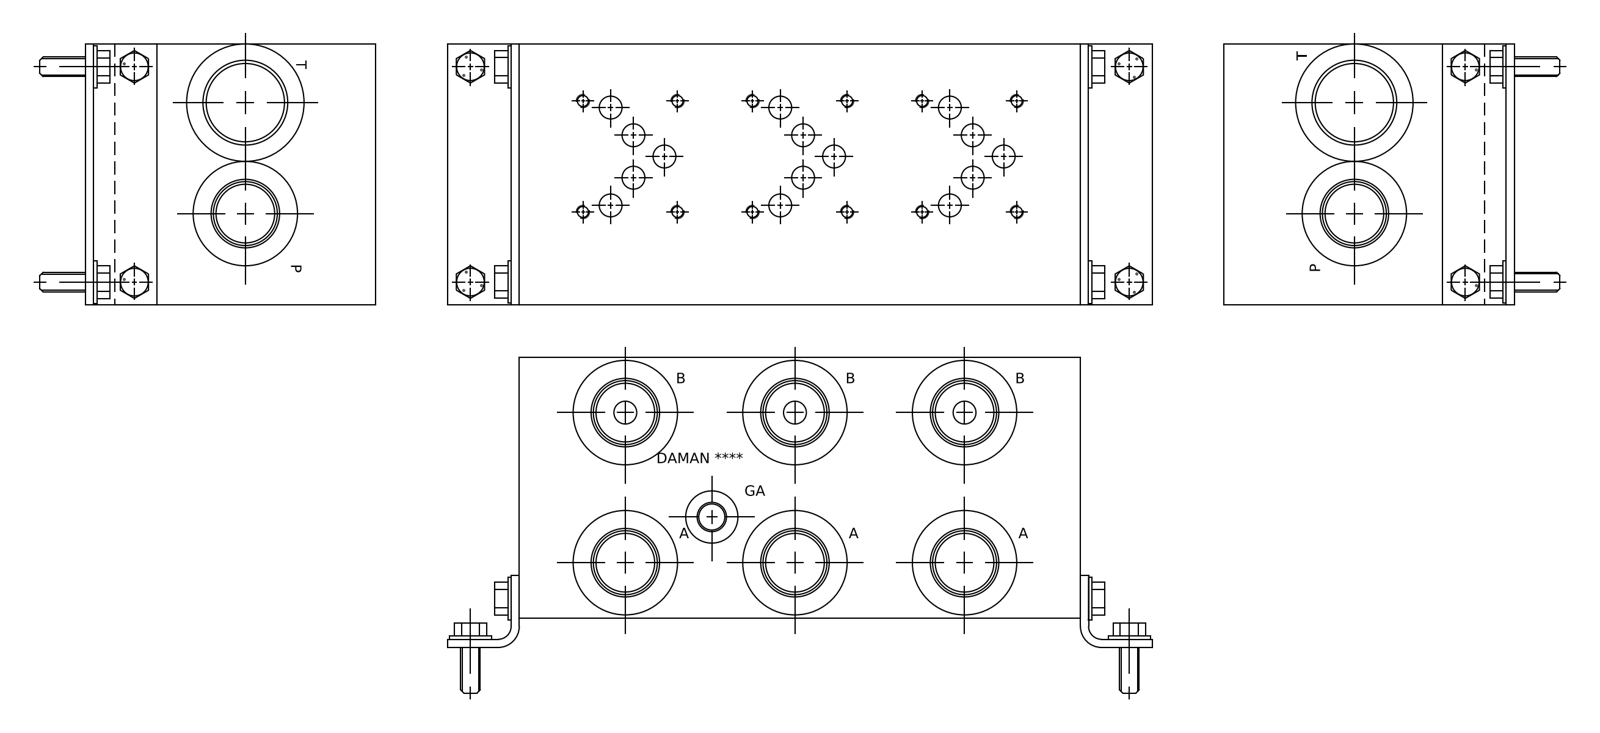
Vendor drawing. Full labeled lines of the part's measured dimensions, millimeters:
Part name (STEP PRODUCT): Part_AD05JP033S_3D
STEP written by: Autodesk Inventor 2020 (AUTOMOTIVE_DESIGN)
Units: millimetres
Bodies: 1 solid, 783 faces (396 planar, 108 cylindrical, 279 other)
Overall size (bounding box): 273.05 × 127 × 127
Volume: 4 040 000 mm³ · Surface area: 221 109 mm²
Round holes (diameter × count): ⌀5.11 ×12, ⌀6.35 ×12, ⌀31.27 ×7, ⌀33.76 ×7, ⌀49.12 ×7, ⌀10.31 ×6, ⌀11.13 ×6, ⌀28.57 ×6, ⌀33.35 ×6, ⌀35.51 ×6, ⌀9.53 ×5, ⌀7.92 ×2
Main face-to-face distances: 127, 273.05, 0.79, 126.21, 272.26, 271.47, 19.05, 19.84, 107.16, 253.21
Hole centre spacings: 82.55, 46.05, 53.97, 82.62, 52.57, 60.33, 70.95, 165.17
